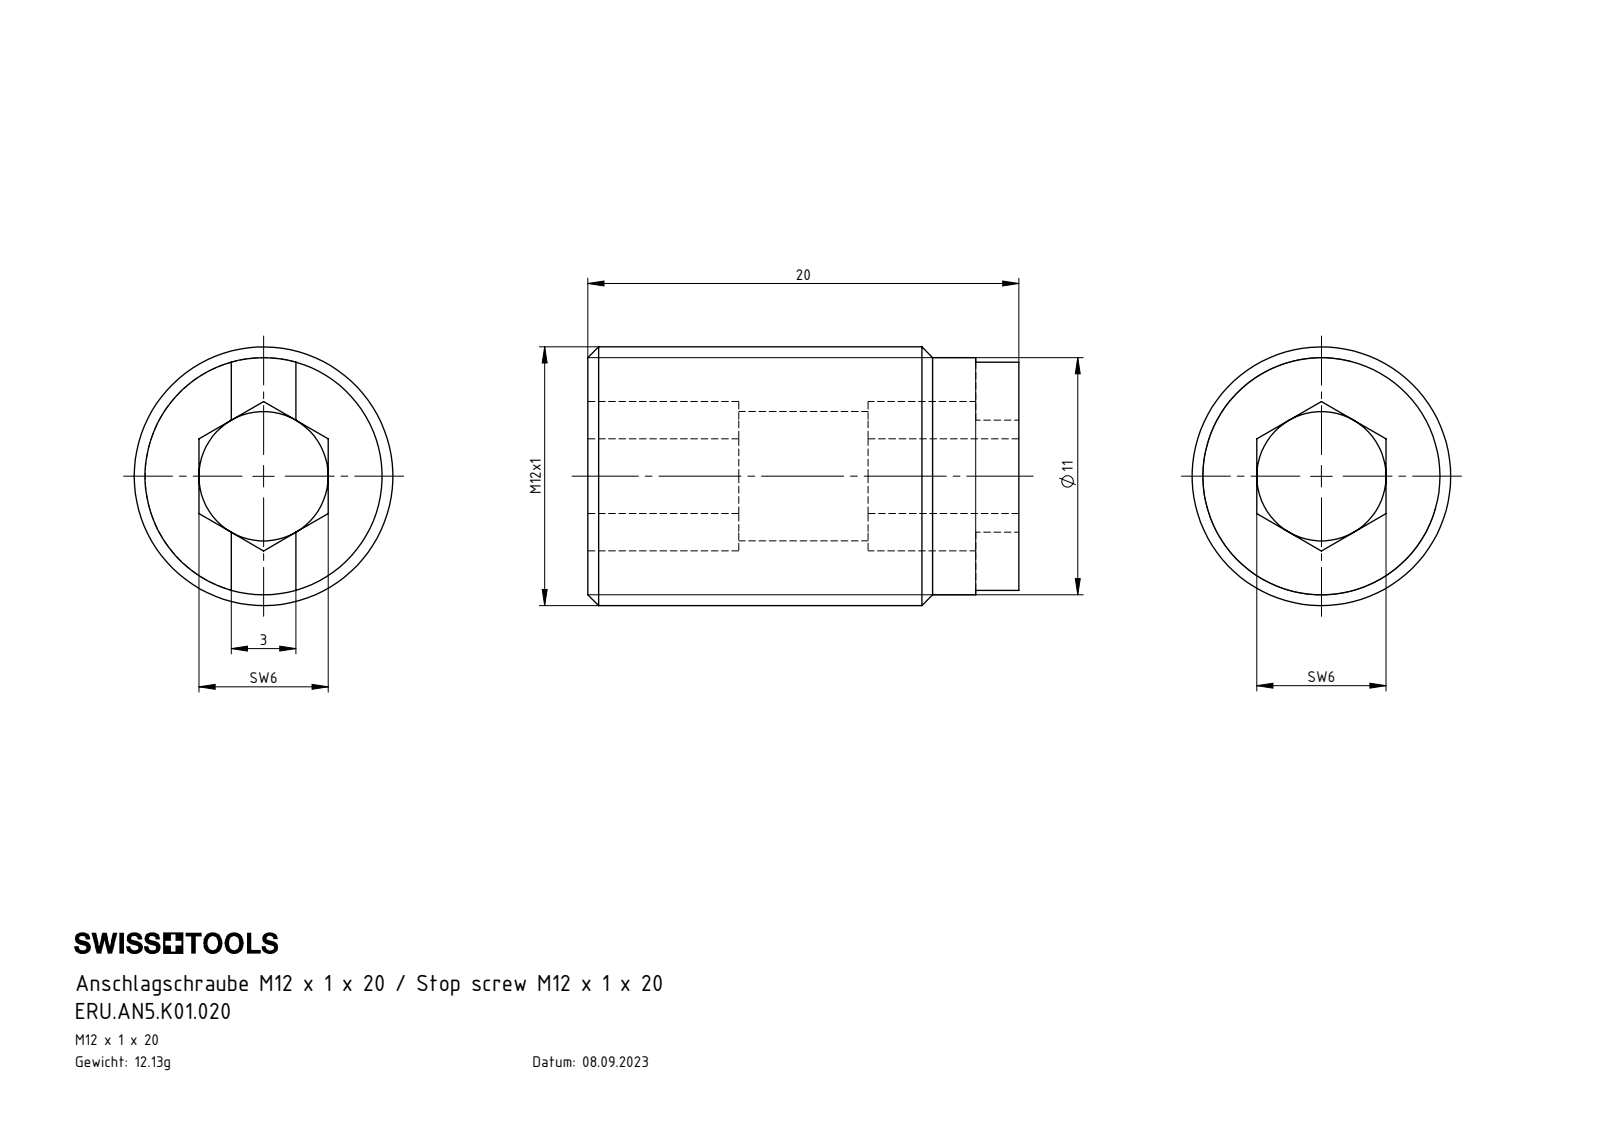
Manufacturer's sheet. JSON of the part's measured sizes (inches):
{"part_name": "ERU.AN5.K01.020", "step_written_by": "SolidWorks 2017 (AUTOMOTIVE_DESIGN)", "units": "inches", "bodies": {"solids": 1, "faces": 43, "planar": 33, "cylindrical": 6, "other": 4}, "overall_size": [0.787, 0.472, 0.472], "volume_in3": 0.094, "surface_area_in2": 1.996, "round_holes": [[0.236, 1]], "round_bosses_or_shafts": [[0.472, 1], [0.433, 1]], "face_to_face_distances": [0.236, 0.787, 0.059, 0.177, 0.709, 0.079, 0.118, 0.276, 0.512, 0.433]}
